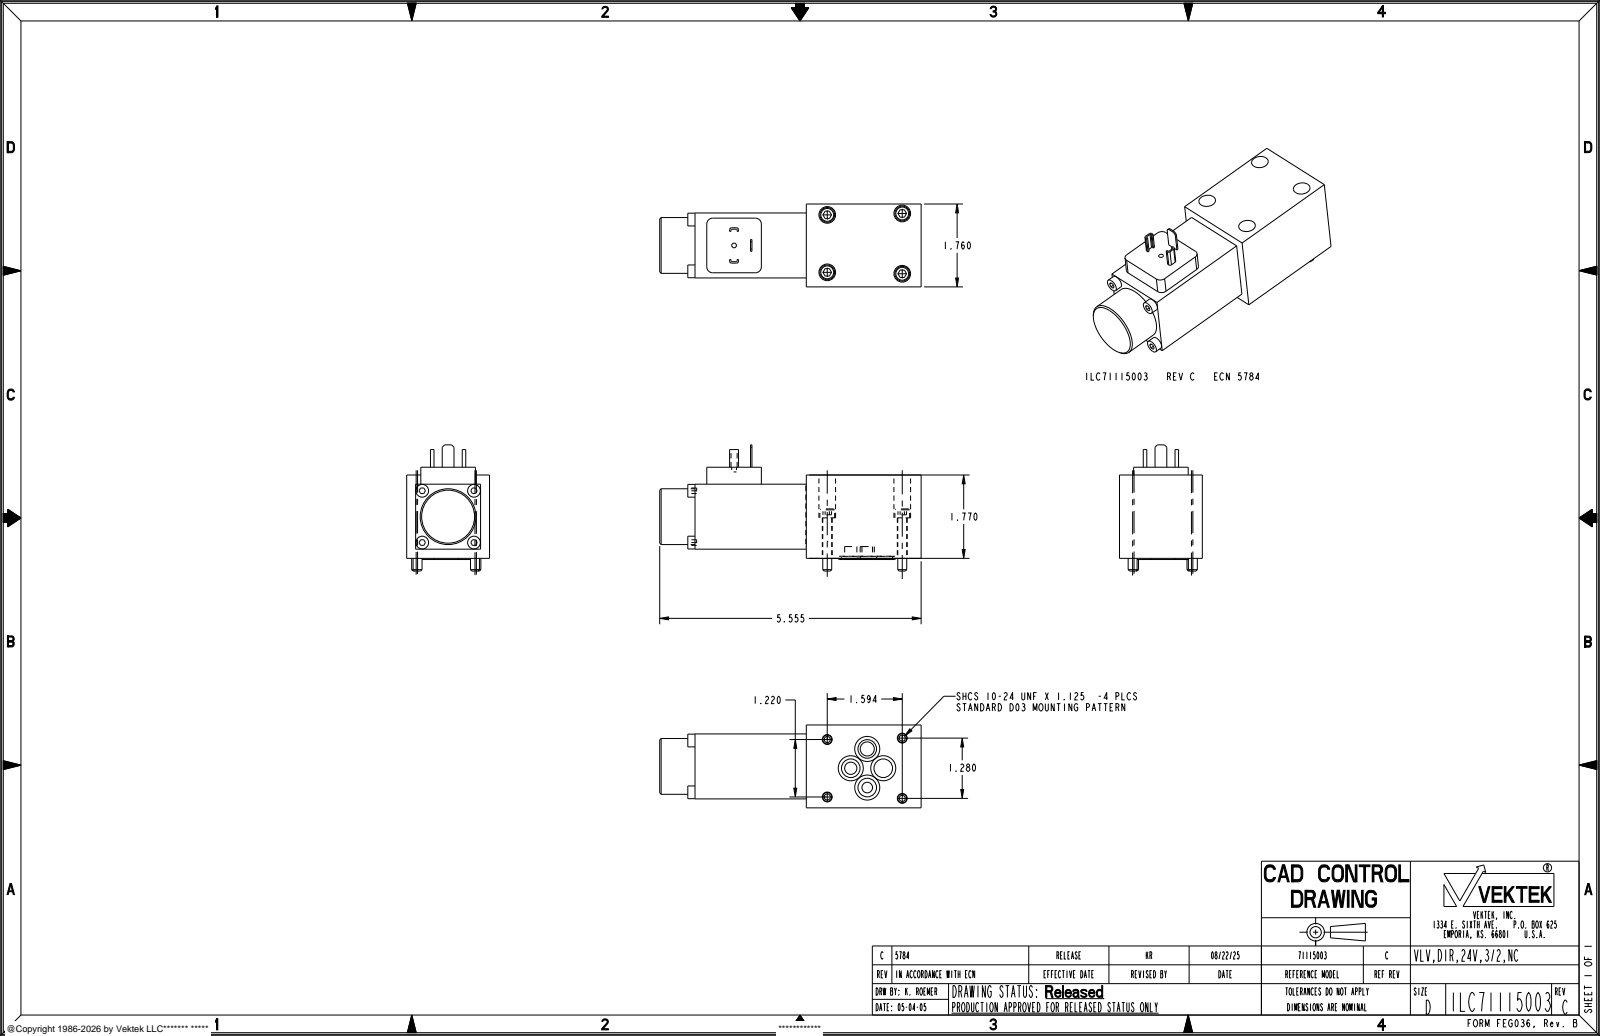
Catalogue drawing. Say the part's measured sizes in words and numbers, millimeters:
The part is named "ILC71115003". Its 3-D file was written by "PRO/ENGINEER BY PARAMETRIC TECHNOLOGY CORPORATION, 2007460 (AUTOMOTIVE_DESIGN_CC2)". It is 1 solid with 285 faces: 162 planar, 93 cylindrical and 30 other. Overall it measures 143.6 by 89 by 44.7 millimeters. Its volume is 247 000 cubic millimeters and its surface area 41 260 square millimeters. Round holes: 4 of diameter 5.3, 4 of diameter 9, 4 of diameter 12.4, 1 of diameter 5.7, 1 of diameter 6.6, 1 of diameter 7.6, 1 of diameter 11.4, 1 of diameter 33.4. Round bosses or shafts: 4 of diameter 8, 4 of diameter 6.9, 4 of diameter 4.8, 1 of diameter 32.1, 1 of diameter 30.1, 1 of diameter 21.7, 1 of diameter 16.7, 1 of diameter 3.8. Partial cylindrical surfaces (rounded edges, fillets, slot ends): 13 of radius 1.3, 4 of radius 0.4, 4 of radius 1, 4 of radius 3.2. The main face-to-face distances are 4.8, 39.9, 40, 5, 35.1, 44.7, 45, 3.8, 36.1, 8.6. The hole center spacings are 13.5, 13.7, 19.2, 19.8, 20, 22.2, 32.2, 32.7.
